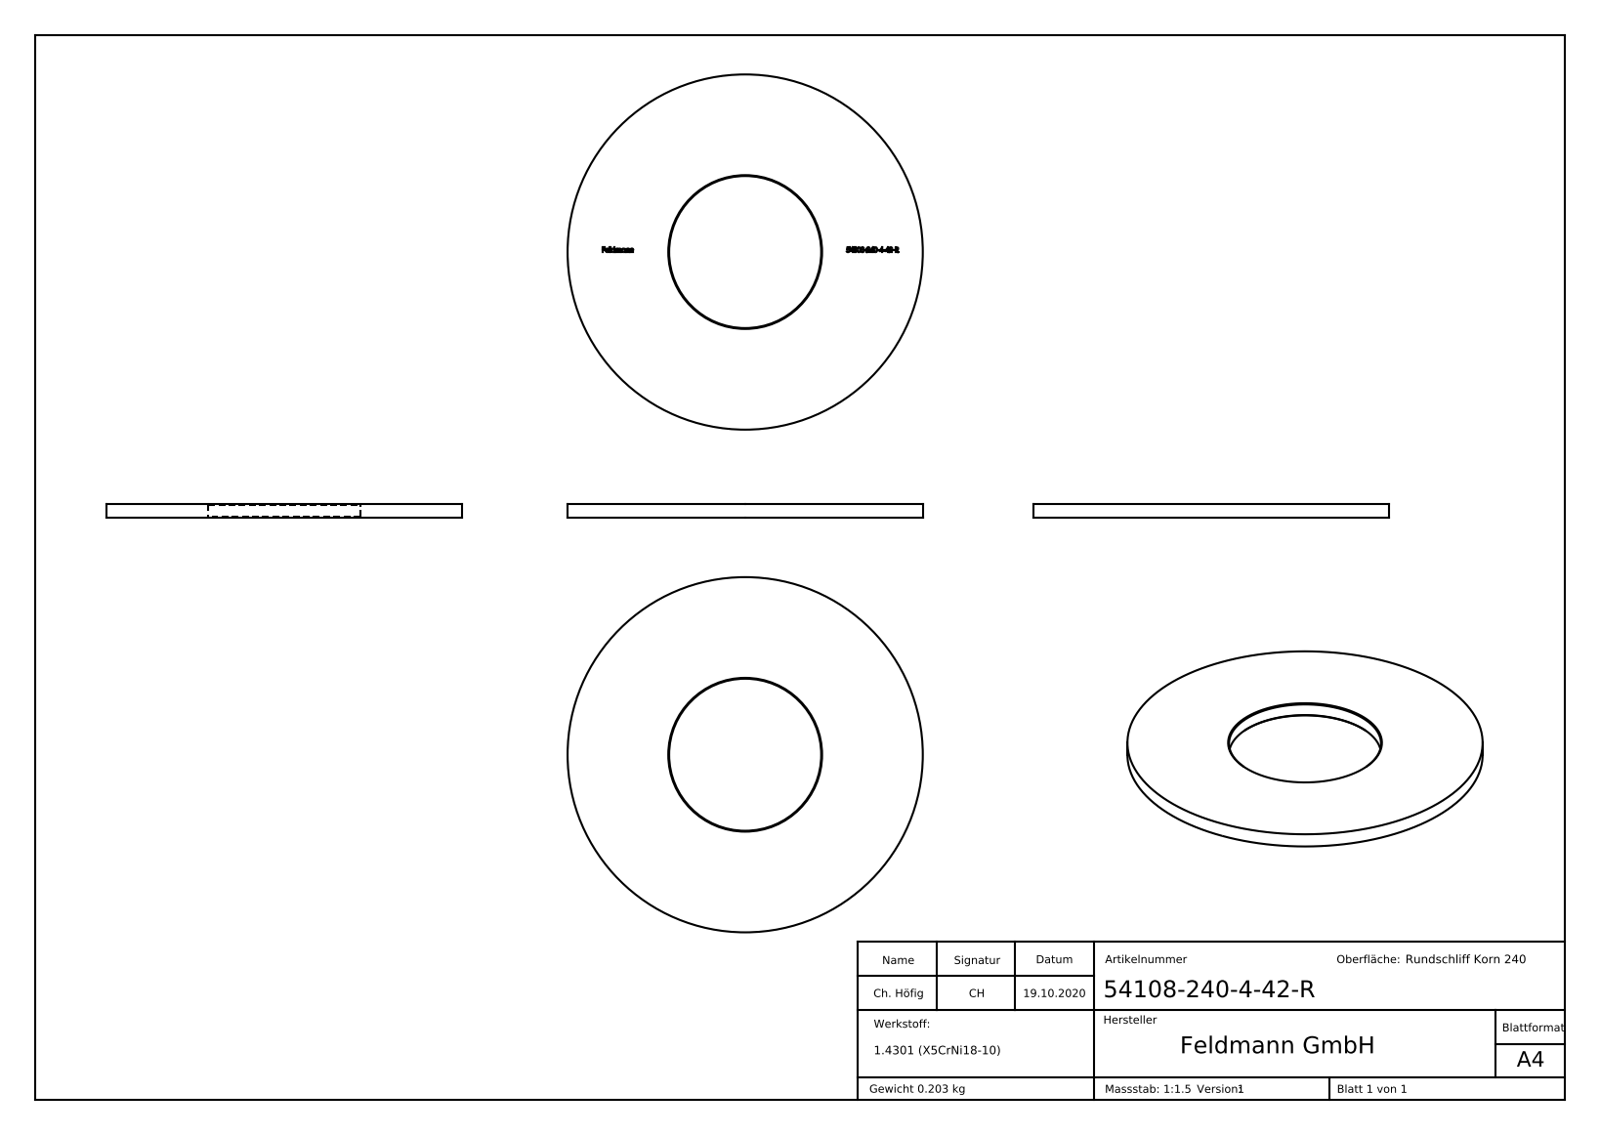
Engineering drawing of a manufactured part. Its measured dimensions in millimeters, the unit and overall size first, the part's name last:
Units: millimetres
Overall size (bounding box): 100 × 100 × 4
Round holes (diameter × count): ⌀42.8 ×1
Round bosses / shafts (diameter × count): ⌀100 ×1
Main face-to-face distances: 4, 3.9, 0.44, 80.34, 2.02, 0.58, 0.31, 0.88, 69.03, 2.14
Volume: 25 652 mm³ · Surface area: 14 598 mm²
Bodies: 1 solid, 311 faces (195 planar, 4 cylindrical, 112 other)
Part name (STEP PRODUCT): 54108-240-4-42-R
STEP written by: SolidWorks 2018 (CONFIG_CONTROL_DESIGN)
